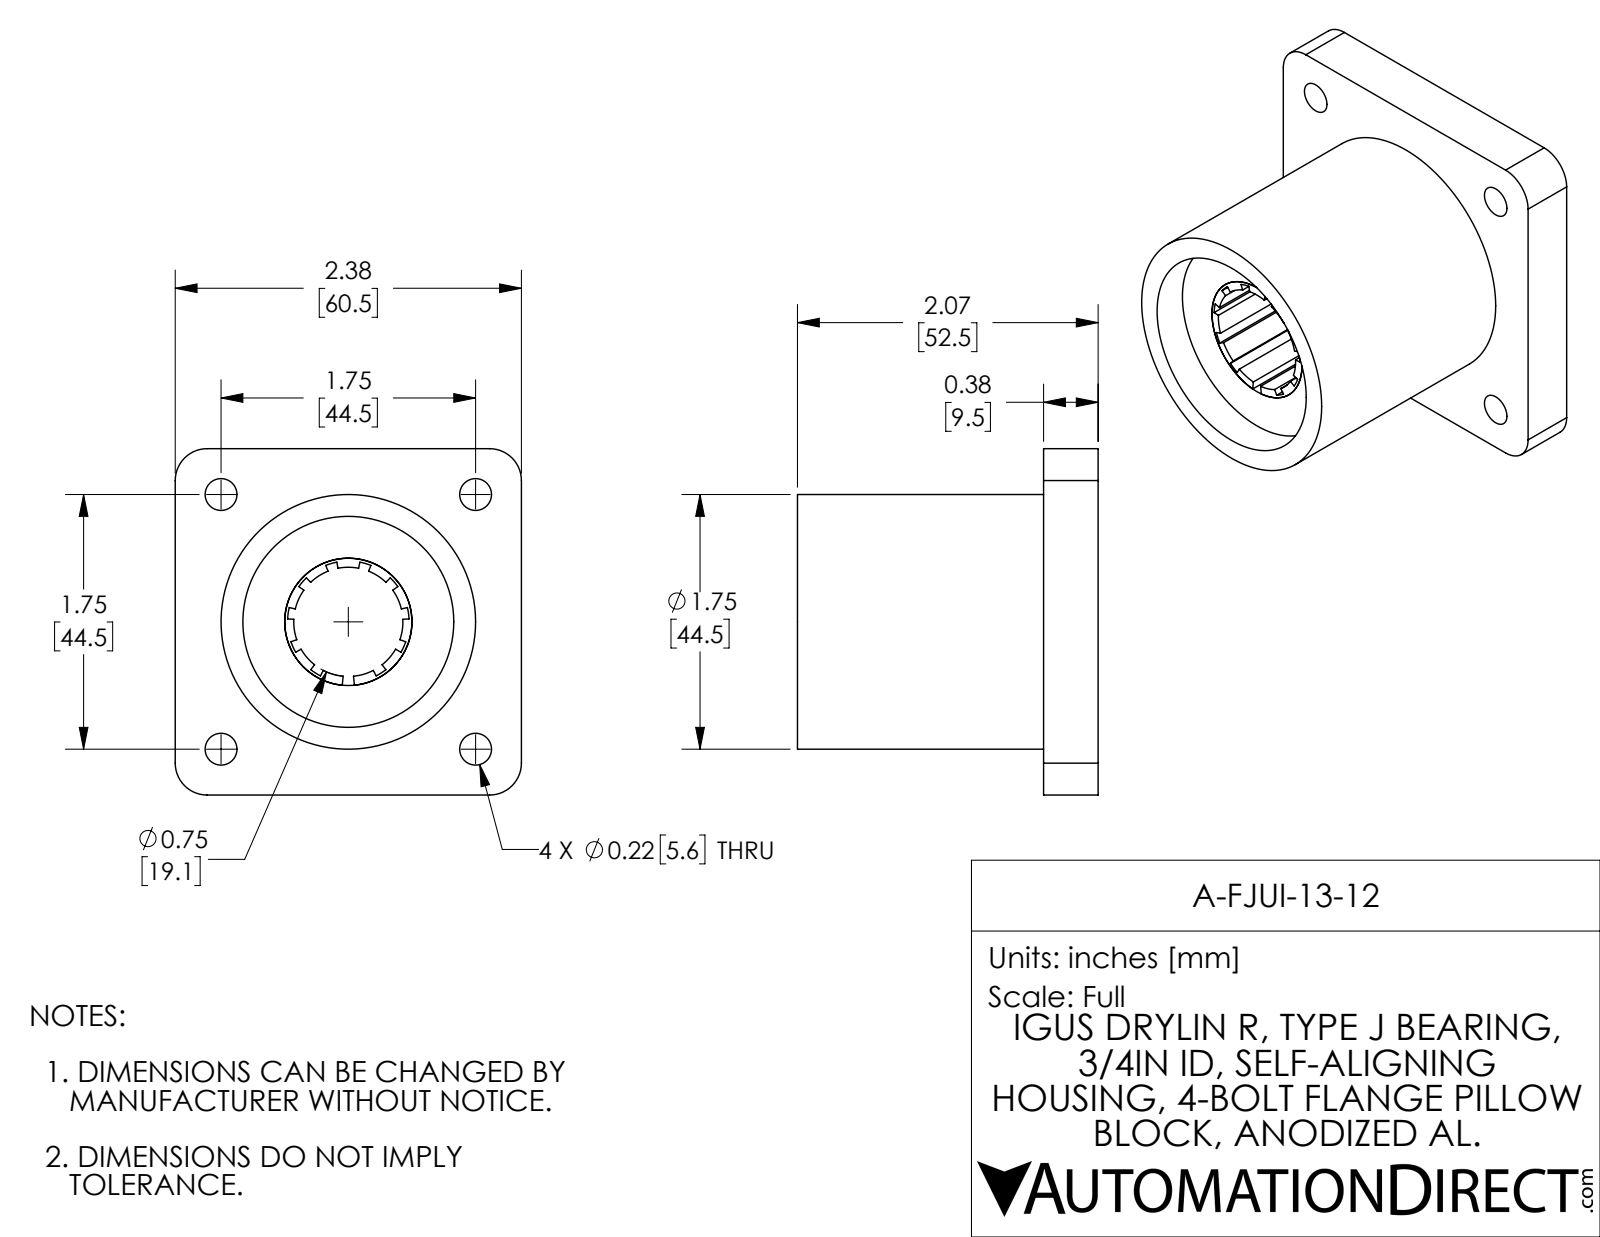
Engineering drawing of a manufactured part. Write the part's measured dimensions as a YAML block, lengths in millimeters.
part_name: "A-FJUI-13-12"
step_written_by: "SolidWorks 2017 (AUTOMOTIVE_DESIGN)"
units: millimeters
bodies: {solids: 2, faces: 135, planar: 76, cylindrical: 59, other: 0}
overall_size: [60.5, 60.5, 52.5]
volume: 74840
surface_area: 25860
round_holes:
  - {diameter: 5.6, count: 4}
  - {diameter: 36.8, count: 1}
round_bosses_or_shafts:
  - {diameter: 44.5, count: 1}
  - {diameter: 22.2, count: 1}
  - {diameter: 3.4, count: 1}
partial_cylinders:
  - {radius: 5.6, count: 4}
  - {radius: 9.5, count: 1}
  - {radius: 10.6, count: 1}
  - {radius: 11.9, count: 1}
face_to_face_distances: [9.5, 46.3, 6.2, 60.5, 36.7, 3.3, 40, 52.5, 43, 23.9]
hole_center_spacings: [31.4, 44.5, 62.9]
